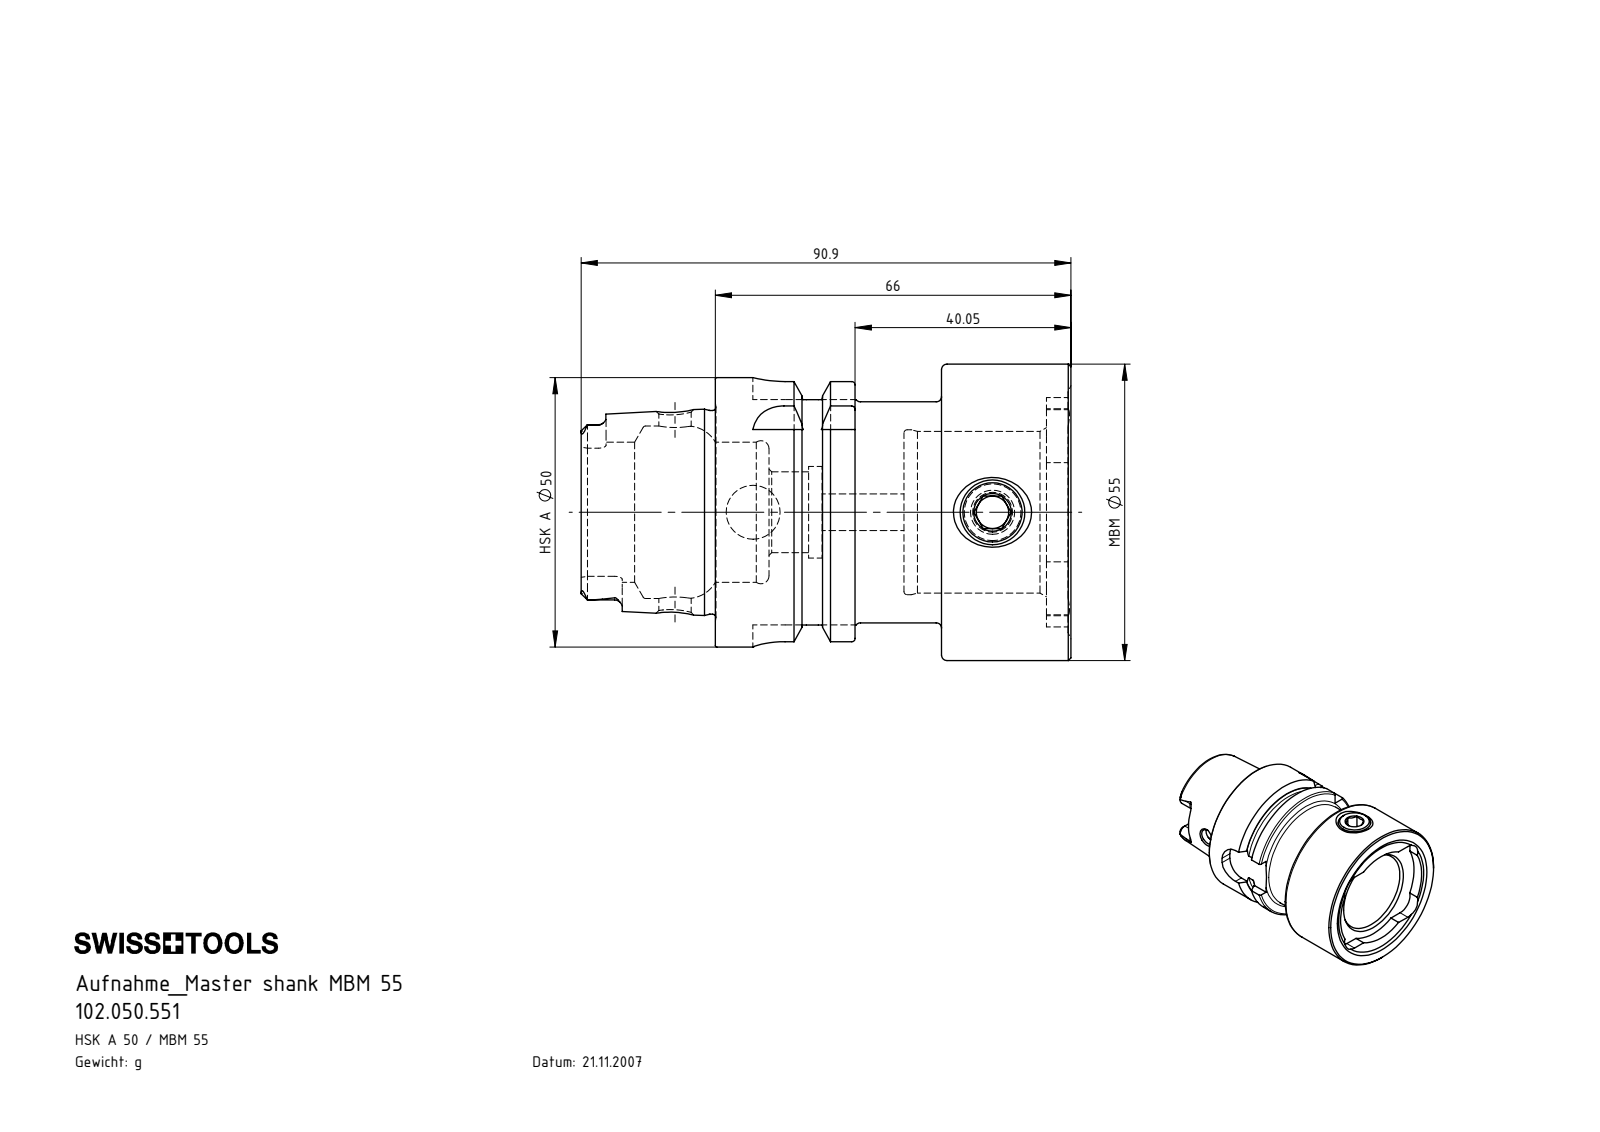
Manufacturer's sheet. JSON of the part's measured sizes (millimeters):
{"part_name": "HA5-MB5.K01.066_B_Fertigbearbeitung; HA5-MB5.K01.066_B; MB5-ER1.001.017_A; 102.050.551", "step_written_by": "SolidWorks 2017 (AUTOMOTIVE_DESIGN)", "units": "millimeters", "bodies": {"solids": 2, "faces": 229, "planar": 72, "cylindrical": 68, "other": 89}, "overall_size": [90.9, 55, 55], "volume_mm3": 101758, "surface_area_mm2": 27543, "round_holes": [[6, 2], [6.8, 1], [10, 1], [11, 1], [15, 1], [17, 1], [26, 1], [30, 1], [30.6, 1], [32, 1]], "round_bosses_or_shafts": [[55, 1], [50, 1], [42.95, 1], [41, 1], [37.81, 1], [12, 1]], "partial_cylinders_radius": [[1.4, 6], [2.38, 4], [5.2, 4], [6, 4], [18.5, 1], [21.27, 1]], "face_to_face_distances": [7, 35, 42, 66, 31, 24, 61.45, 26.45, 19.45, 4.55], "hole_center_spacings": [44.45]}
